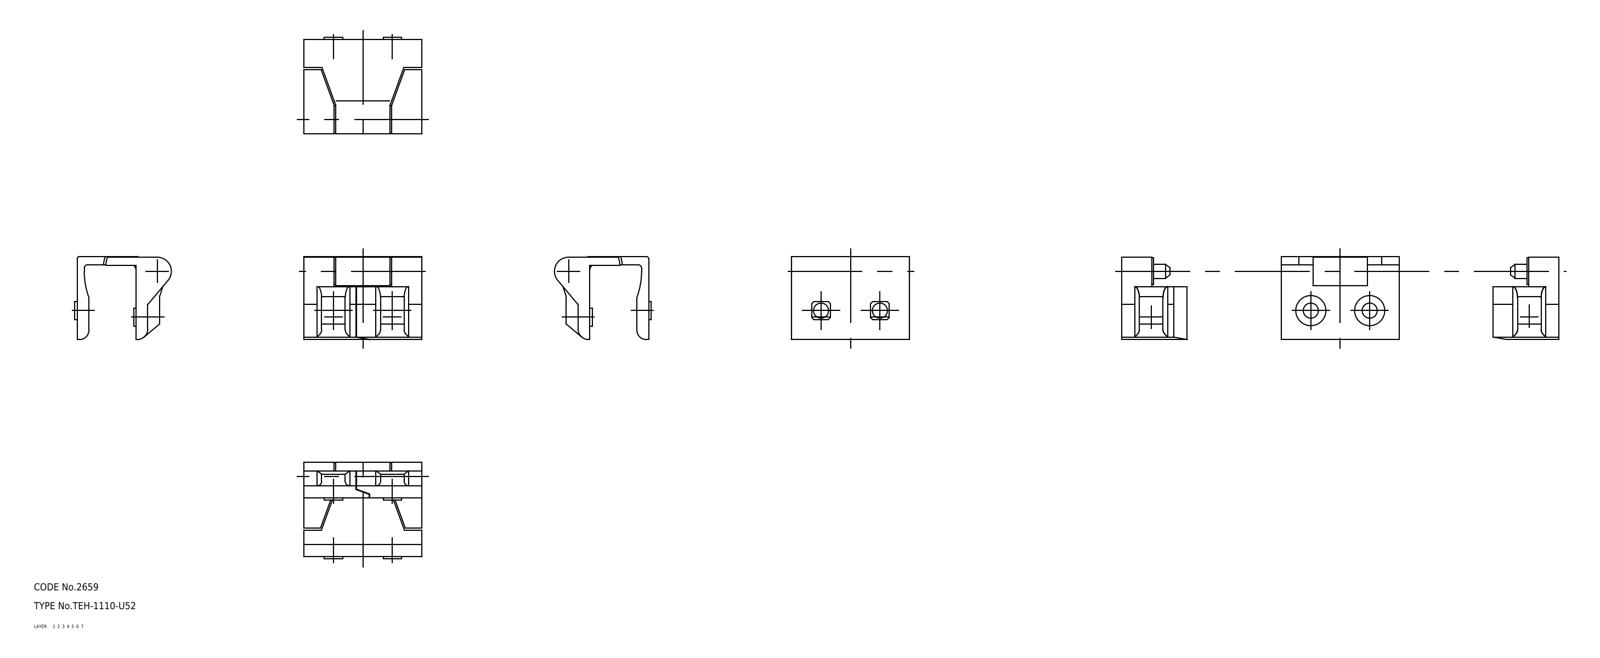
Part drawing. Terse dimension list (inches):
name: 67115931; 67115944; 67115957
written by: CADfix (AUTOMOTIVE_DESIGN)
unit: in
bodies: 3 solids, 153 faces (0 planar, 0 cylindrical, 153 other)
size: 1.969 × 1.614 × 1.39
volume: 1.63 in³; area: 21.97 in²
